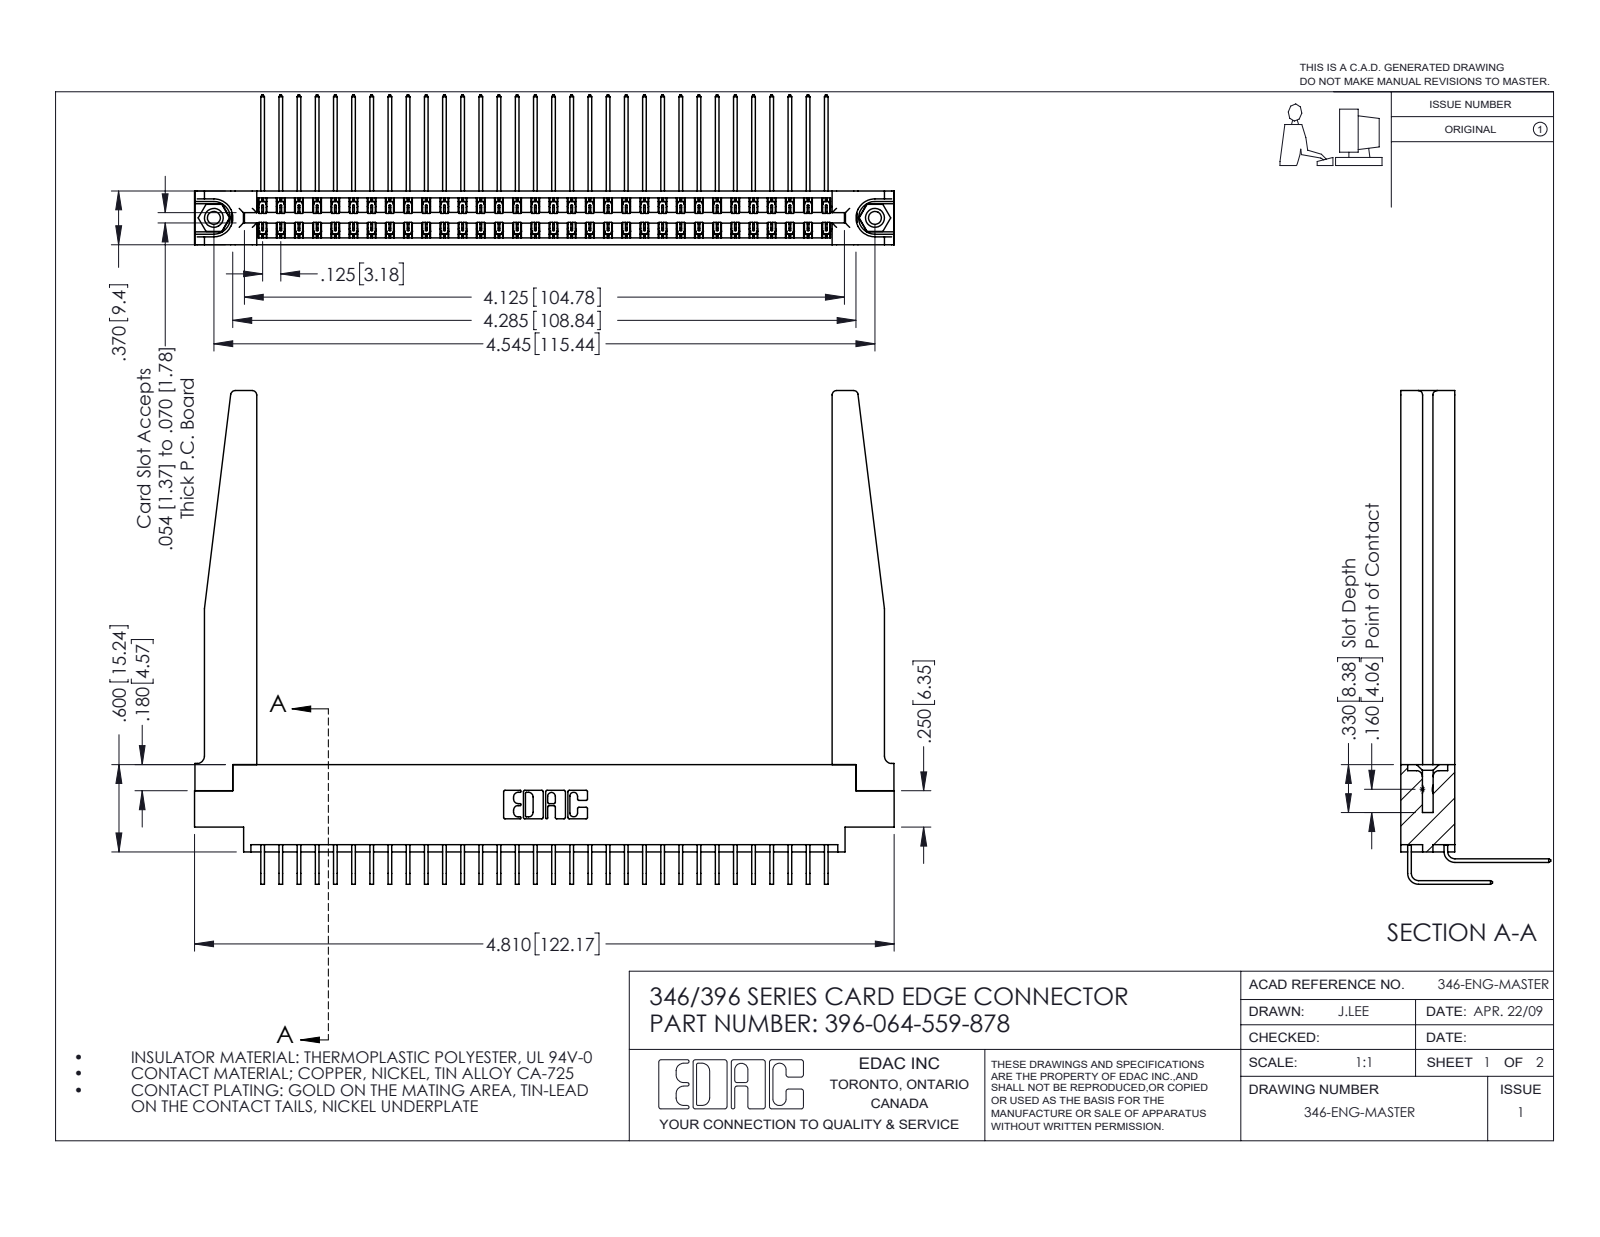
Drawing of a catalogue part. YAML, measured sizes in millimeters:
part_name: "345-250-001_345-250-001-102; 346 Part_0.170 Offset - 0.156 Dia-TH; 346-220-078_345-220-078; 345-292-001_559 Tail - 2 (+2 more)"
step_written_by: "SolidWorks 2016 (CONFIG_CONTROL_DESIGN)"
units: millimeters
bodies: {solids: 69, faces: 3816, planar: 2590, cylindrical: 1174, other: 52}
overall_size: [122.2, 86.2, 26.2]
volume: 18960
surface_area: 24900
round_holes:
  - {diameter: 2.3, count: 2}
  - {diameter: 3.2, count: 2}
  - {diameter: 4, count: 2}
  - {diameter: 1.6, count: 1}
round_bosses_or_shafts:
  - {diameter: 3.9, count: 2}
partial_cylinders:
  - {radius: 0.2, count: 96}
  - {radius: 0.3, count: 22}
  - {radius: 0.8, count: 8}
  - {radius: 0.2, count: 6}
  - {radius: 0.8, count: 6}
  - {radius: 1.3, count: 4}
  - {radius: 0.7, count: 3}
  - {radius: 0.4, count: 2}
face_to_face_distances: [9.4, 1.2, 8.2, 1.8, 0.6, 3.8, 3.8, 6.4, 7.6, 7]
hole_center_spacings: [6.2, 110.2, 115.4]
